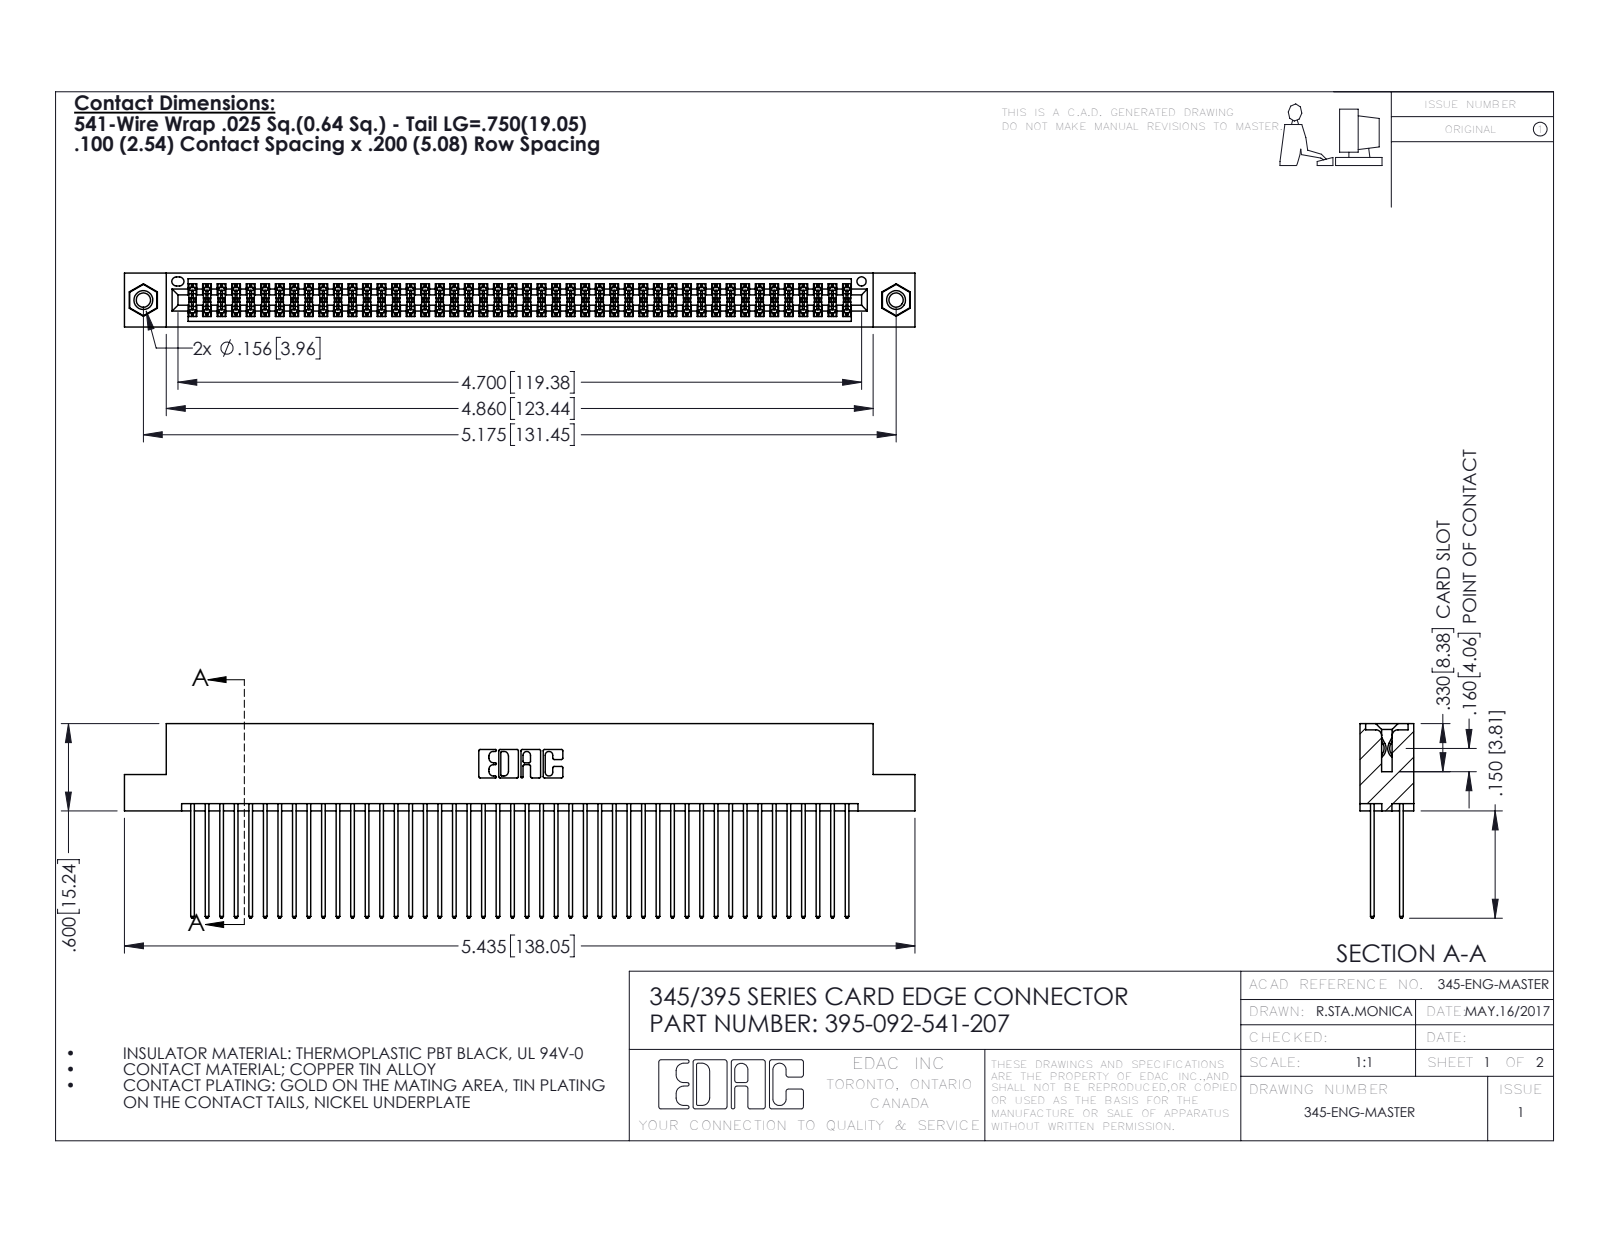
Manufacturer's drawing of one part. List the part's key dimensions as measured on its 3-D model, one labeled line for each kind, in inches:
Part name (STEP PRODUCT): 345-250-001_345-250-005-103; 345 Part_Flush Mounting Lugs - 0.156 Dia-TI; 395-092-541-207; 345-292-001_345-293-141
STEP written by: SolidWorks 2016 (CONFIG_CONTROL_DESIGN)
Units: inches
Bodies: 95 solids, 4786 faces (3148 planar, 1622 cylindrical, 16 other)
Overall size (bounding box): 5.435 × 1.337 × 0.37
Volume: 0.852 in³ · Surface area: 36 in²
Round holes (diameter × count): ⌀0.098 ×2, ⌀0.125 ×2, ⌀0.156 ×2, ⌀0.064 ×1
Round bosses / shafts (diameter × count): ⌀0.155 ×2
Partial cylindrical surfaces — rounded edges, fillets, slot ends (radius × count): R0.006 ×138, R0.01 ×92, R0.01 ×22, R0.007 ×6, R0.031 ×6, R0.026 ×3, R0.014 ×2, R0.019 ×2
Main face-to-face distances: 0.072, 0.298, 0.2, 0.098, 0.272, 0.025, 0.225, 0.37, 0.175, 0.149
Hole centre spacings: 0.27, 4.939, 5.175
